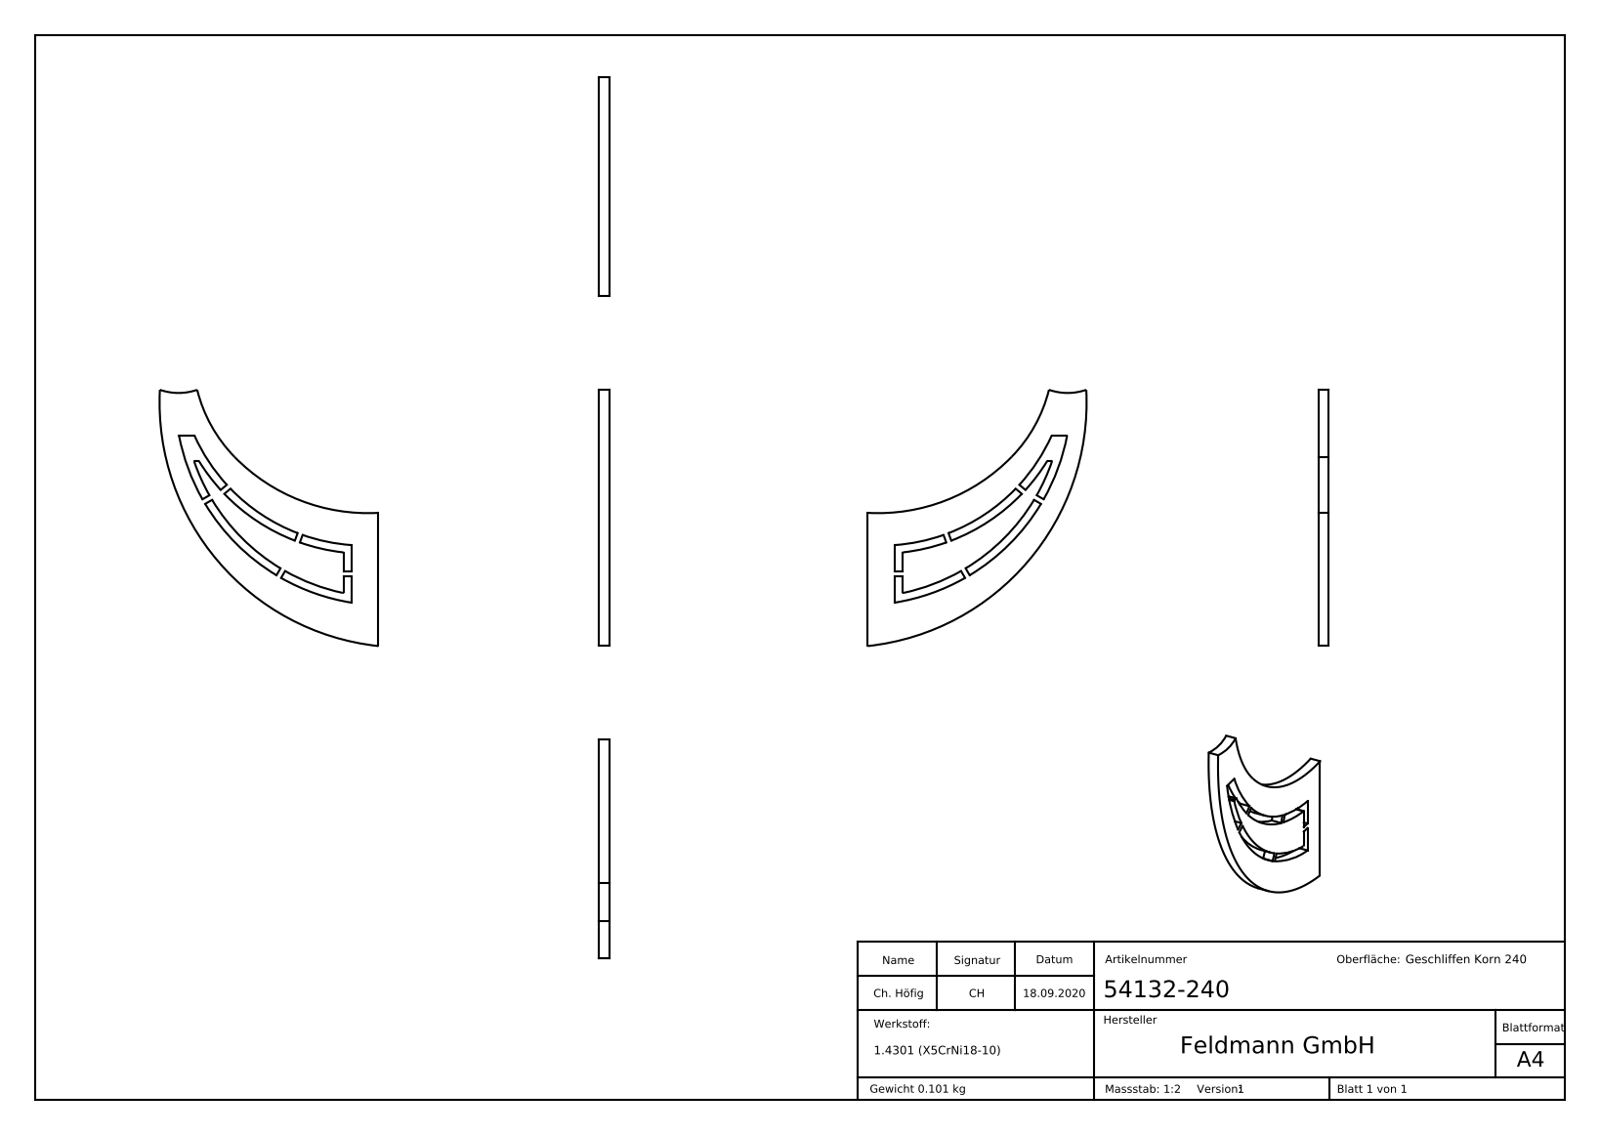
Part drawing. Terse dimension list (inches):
name: 54132-240
written by: SolidWorks 2018 (CONFIG_CONTROL_DESIGN)
unit: in
bodies: 1 solid, 264 faces (153 planar, 20 cylindrical, 91 other)
size: 3.787 × 3.233 × 0.157
volume: 0.78 in³; area: 14.02 in²
rounds: 4× R0.01, 2× R2.756, 1× R0.835, 1× R2.165, 1× R2.874, 1× R2.972, 1× R3.091, 1× R3.622
face distances: 0.157, 0.398, 0.079, 0.516, 0.118, 2.083, 2.004, 1.709, 1.63, 0.374
